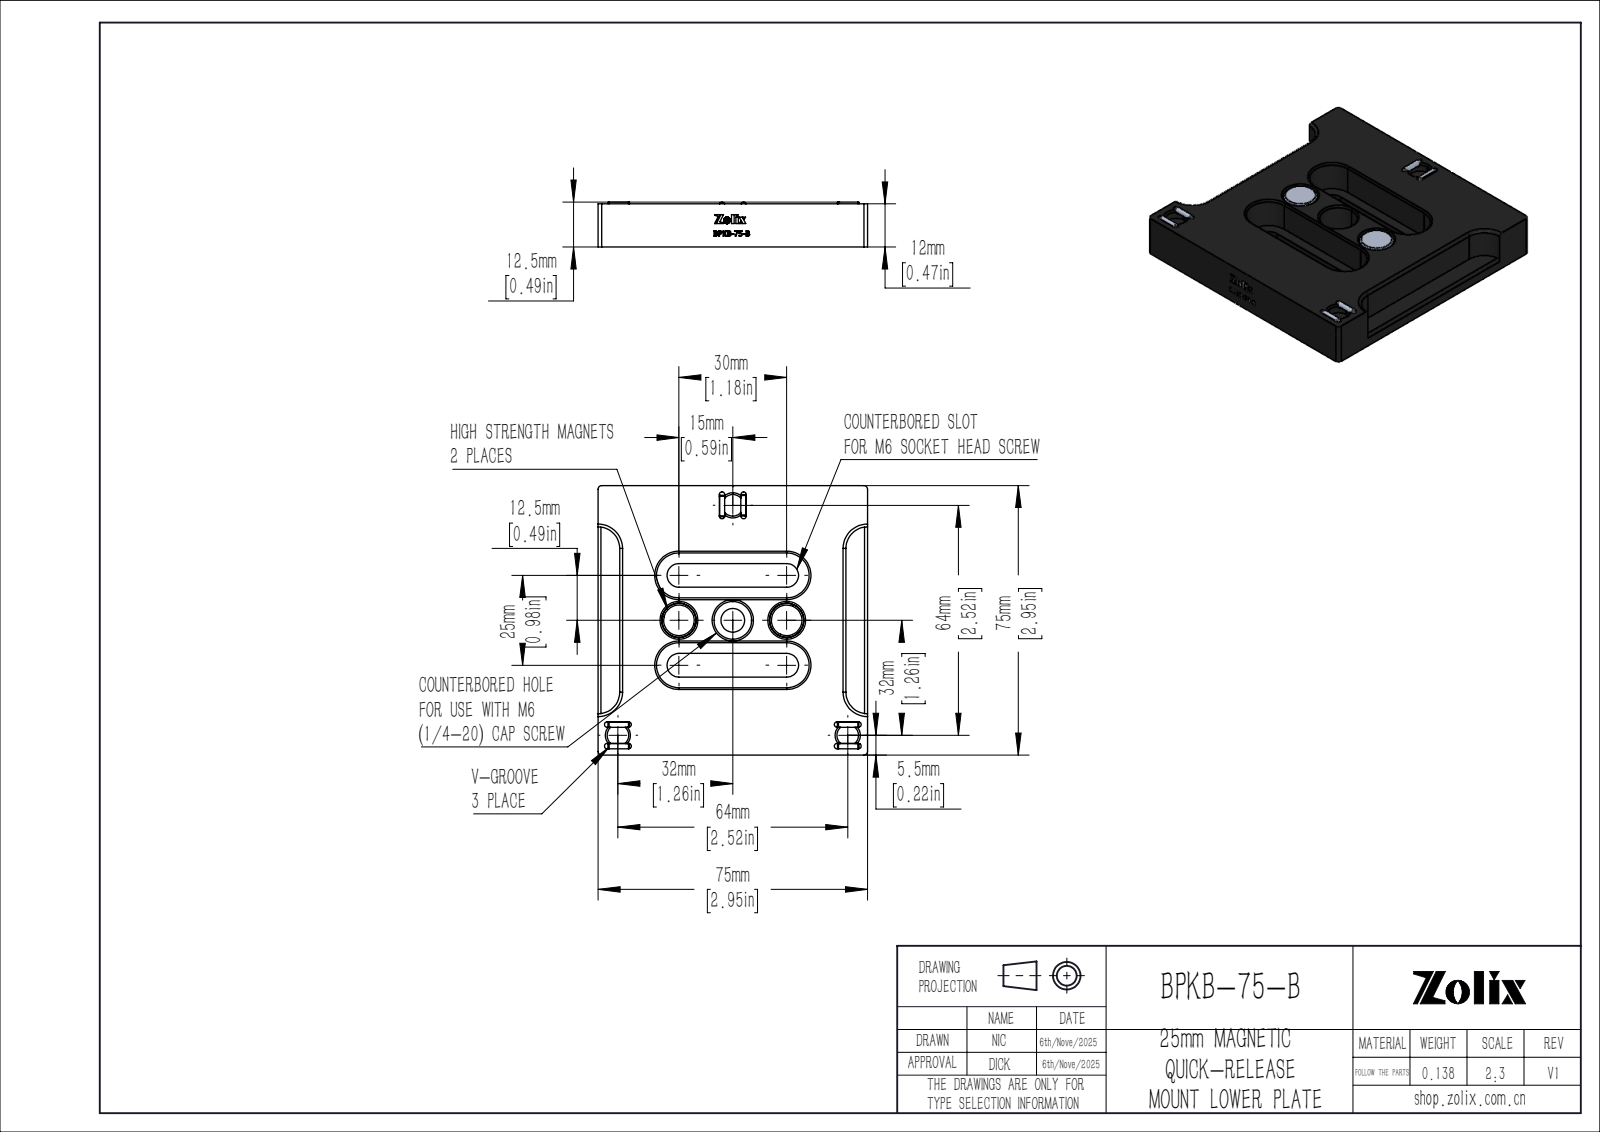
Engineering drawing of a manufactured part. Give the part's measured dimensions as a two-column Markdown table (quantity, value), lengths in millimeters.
| quantity | value |
| --- | --- |
| part name | BPKB-75-B |
| STEP written by | SolidWorks 2020 (CONFIG_CONTROL_DESIGN) |
| units | millimeters |
| bodies | 9 solids, 505 faces (306 planar, 68 cylindrical, 131 other) |
| overall size | 75.01 × 75 × 12.5 |
| volume | 51 199 mm³ |
| surface area | 17 789 mm² |
| round holes (diameter × count) | 6 × 3, 3 × 2, 9.55 × 2, 6.6 × 1, 10.5 × 1 |
| round bosses / shafts (diameter × count) | 1.5 × 4, 9.5 × 2 |
| partial cylindrical surfaces (radius × count) | 0.75 × 12, 0.8 × 4, 1 × 4, 3.3 × 4, 6 × 4, 6.25 × 4 |
| main face-to-face distances | 12, 8.5, 3.5, 6, 69, 74.99, 75.01, 75, 25.01, 2.95 |
| hole center spacings | 15, 35.35, 36.23, 45.25, 56.85, 71.55, 30, 32 |
